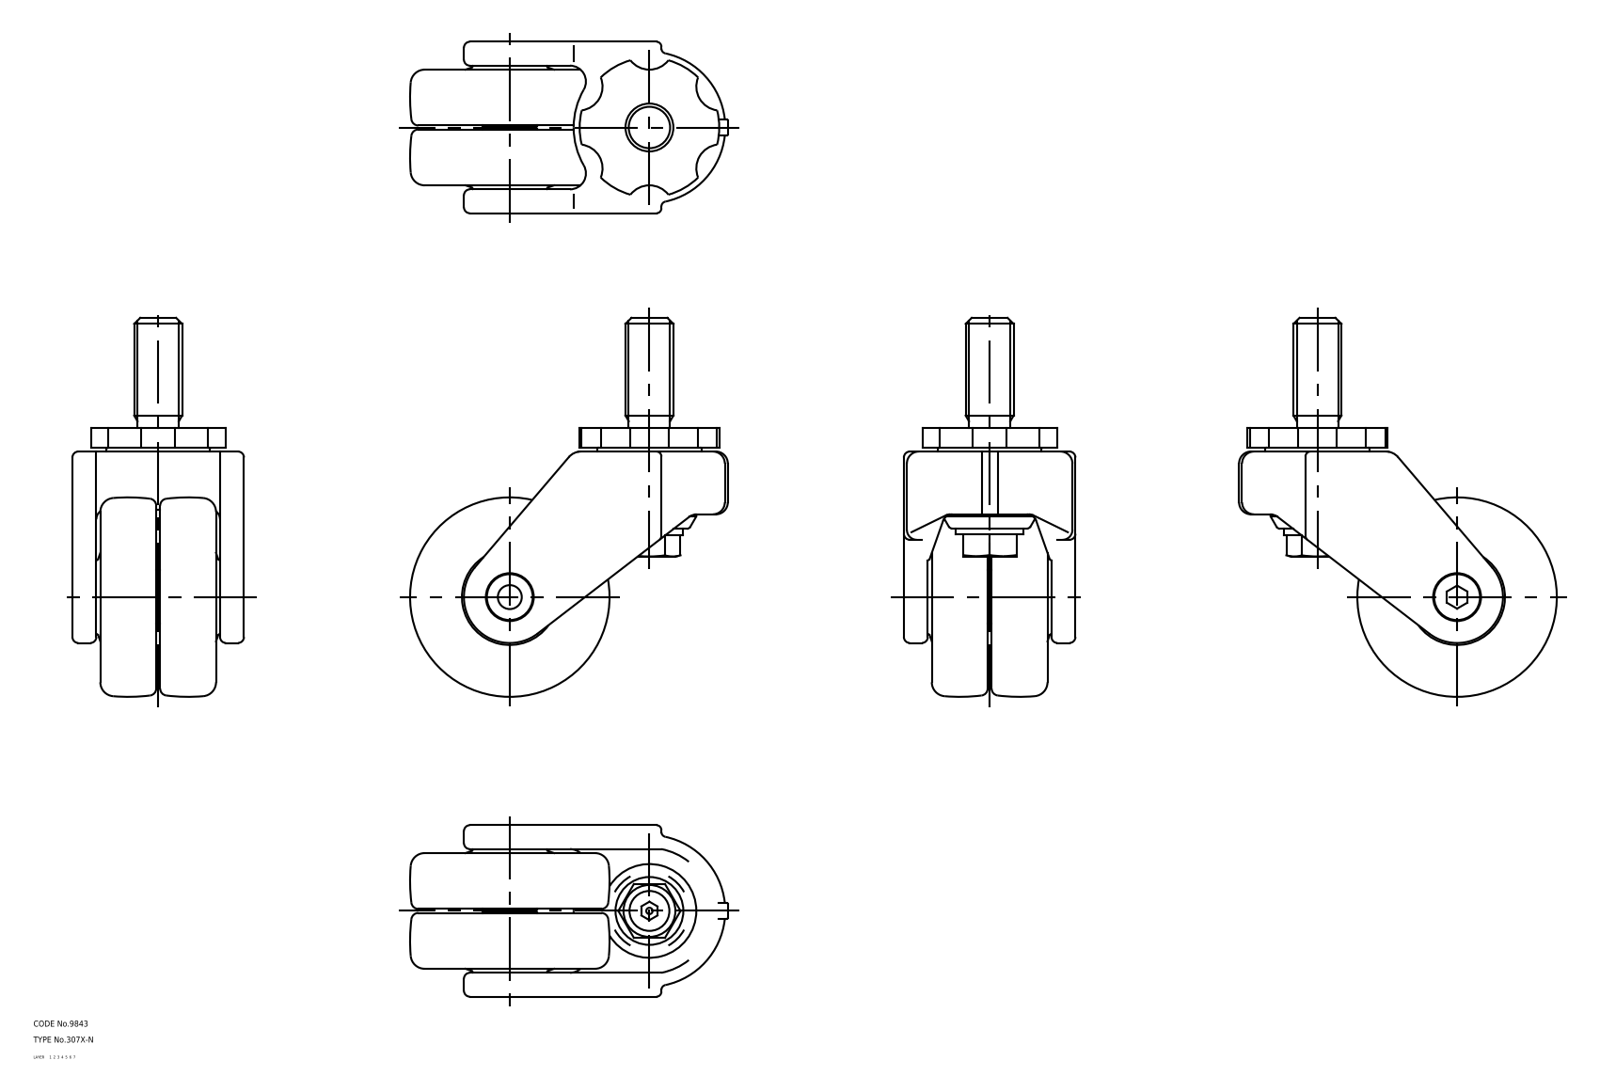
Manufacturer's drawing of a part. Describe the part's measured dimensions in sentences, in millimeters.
The part is named "wheel; main shaft; axle; No_307X_N_24700_36". Its 3-D file was written by "CADfix (AUTOMOTIVE_DESIGN)". It is 4 solids with 232 faces: 0 planar, 0 cylindrical and 232 other. Overall it measures 190 by 159.3 by 86 millimeters. Its volume is 791 513 cubic millimeters and its surface area 116 071 square millimeters.
